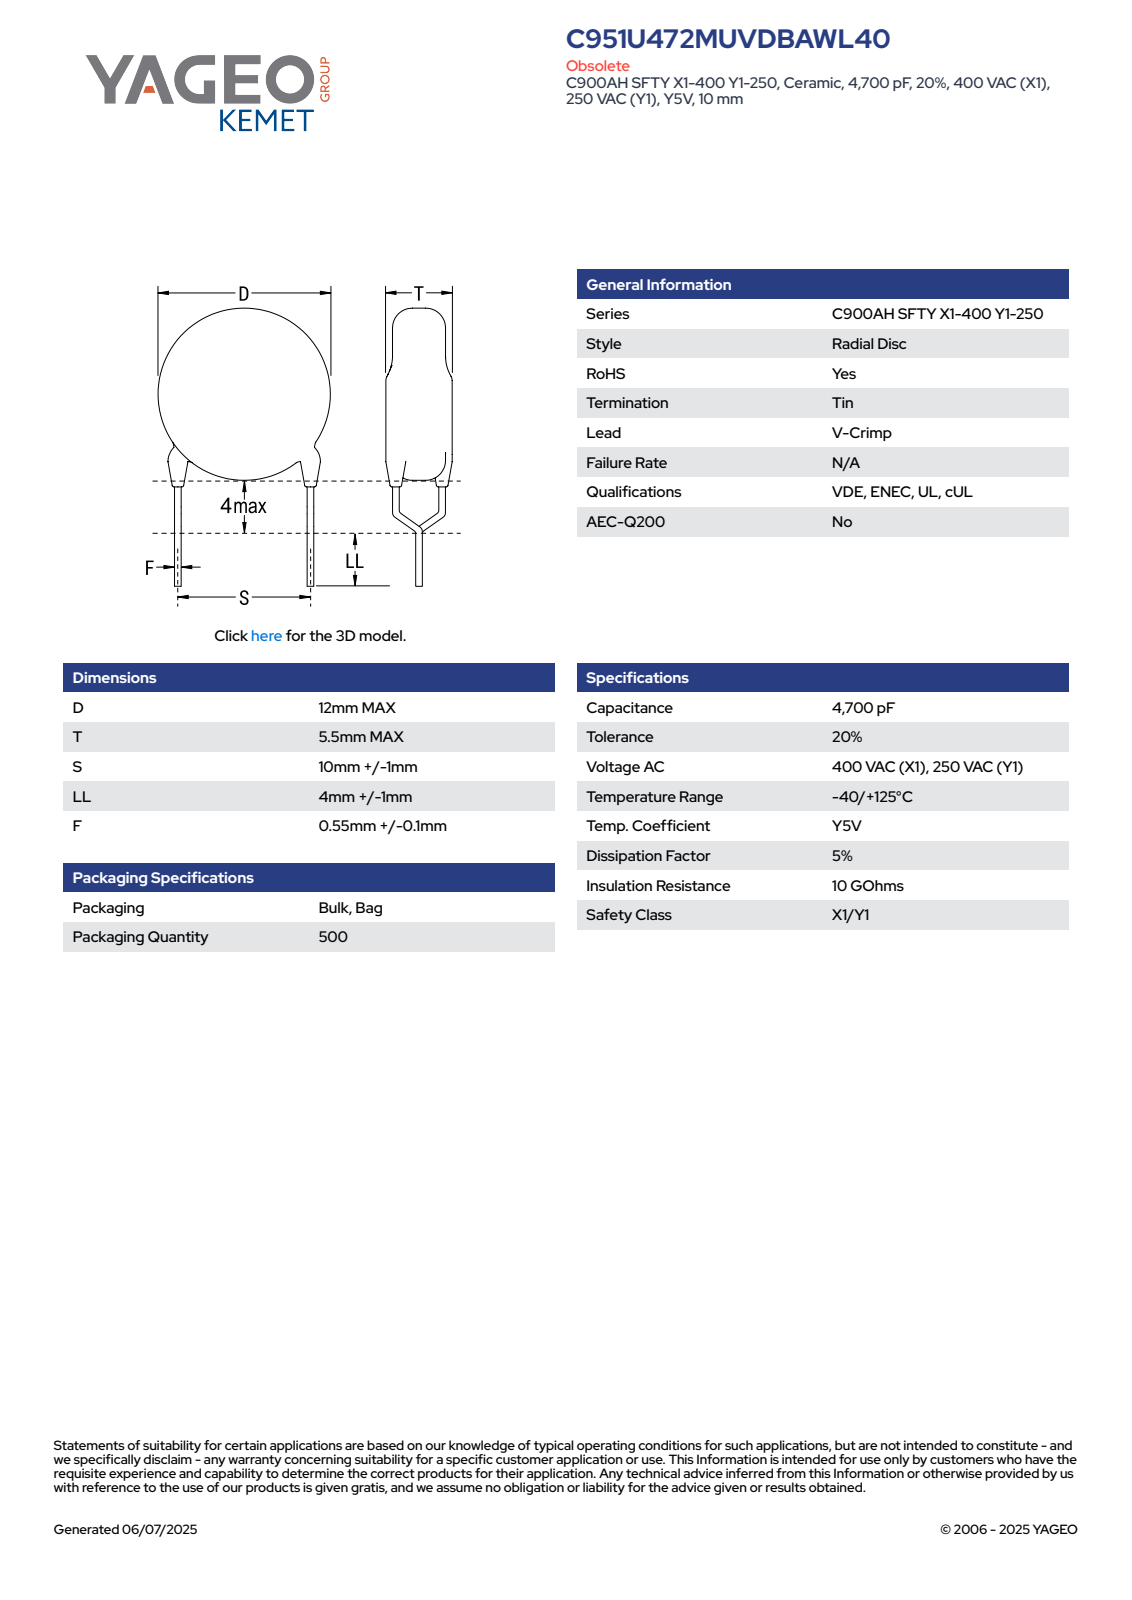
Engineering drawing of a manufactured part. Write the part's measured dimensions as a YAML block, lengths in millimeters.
part_name: "CCD_VCC900_D12T5.5S10LL5F0.65"
step_written_by: "SolidWorks 2014 (AUTOMOTIVE_DESIGN)"
units: millimeters
bodies: {solids: 5, faces: 93, planar: 65, cylindrical: 16, other: 12}
overall_size: [20.8, 12, 5.5]
volume: 616
surface_area: 464
round_bosses_or_shafts:
  - {diameter: 0.65, count: 6}
  - {diameter: 12, count: 1}
face_to_face_distances: [5.5, 7.9, 15.58, 7.68, 14.02, 6.12, 1.56, 0.42, 0.38, 1.26]
